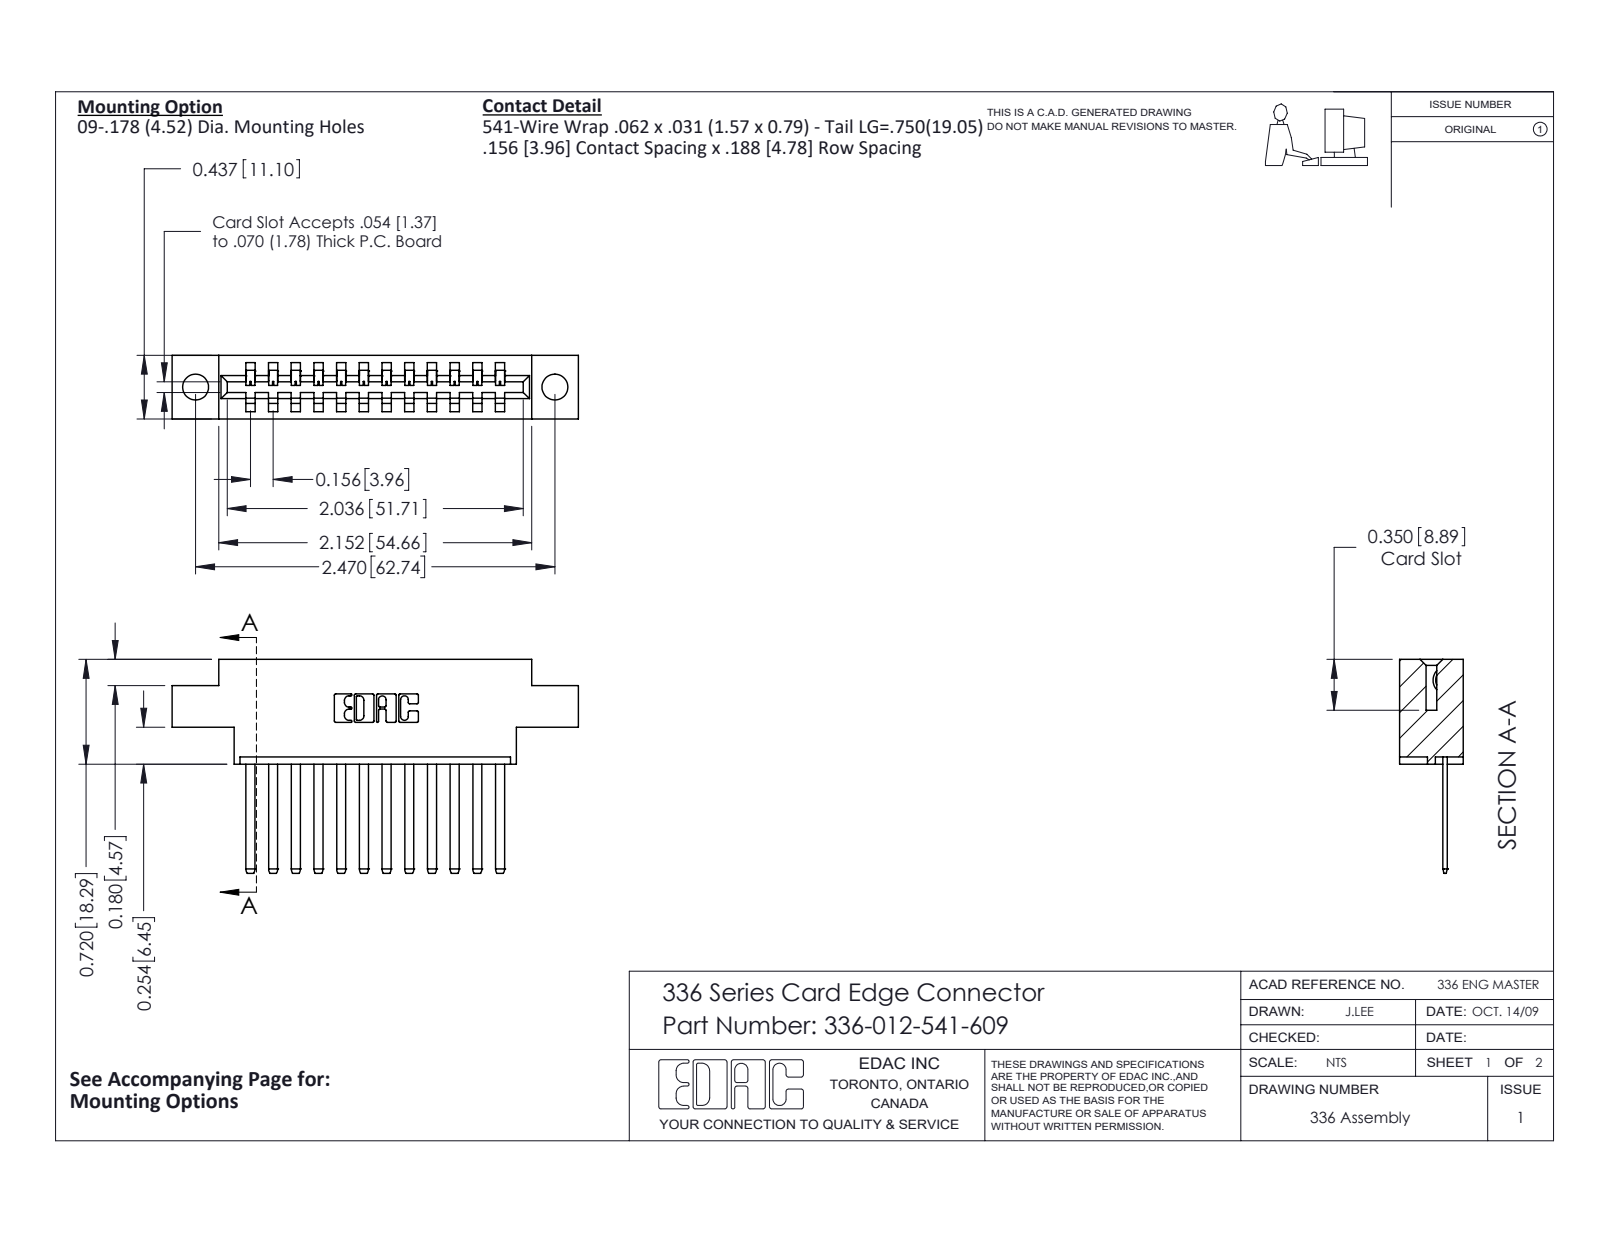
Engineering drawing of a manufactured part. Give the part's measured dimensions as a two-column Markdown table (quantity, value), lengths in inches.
| quantity | value |
| --- | --- |
| part name | 336-012-541-609; 336 Part_Offset - .178 Dia - TH; 336-290-001_336-290-541 |
| STEP written by | SolidWorks 2020 (CONFIG_CONTROL_DESIGN) |
| units | inches |
| bodies | 13 solids, 718 faces (482 planar, 236 cylindrical, 0 other) |
| overall size | 2.793 × 1.47 × 0.437 |
| volume | 0.569 in³ |
| surface area | 15.06 in² |
| round holes (diameter × count) | 0.178 × 2 |
| partial cylindrical surfaces (radius × count) | 0.004 × 24, 0.056 × 24, 0.01 × 22, 0.007 × 6, 0.031 × 6, 0.026 × 3, 0.022 × 2, 0.04 × 2 |
| main face-to-face distances | 0.437, 0.156, 0.624, 0.468, 0.181, 0.312, 0.312, 0.404, 0.256, 0.328 |
| hole center spacings | 2.47 |
